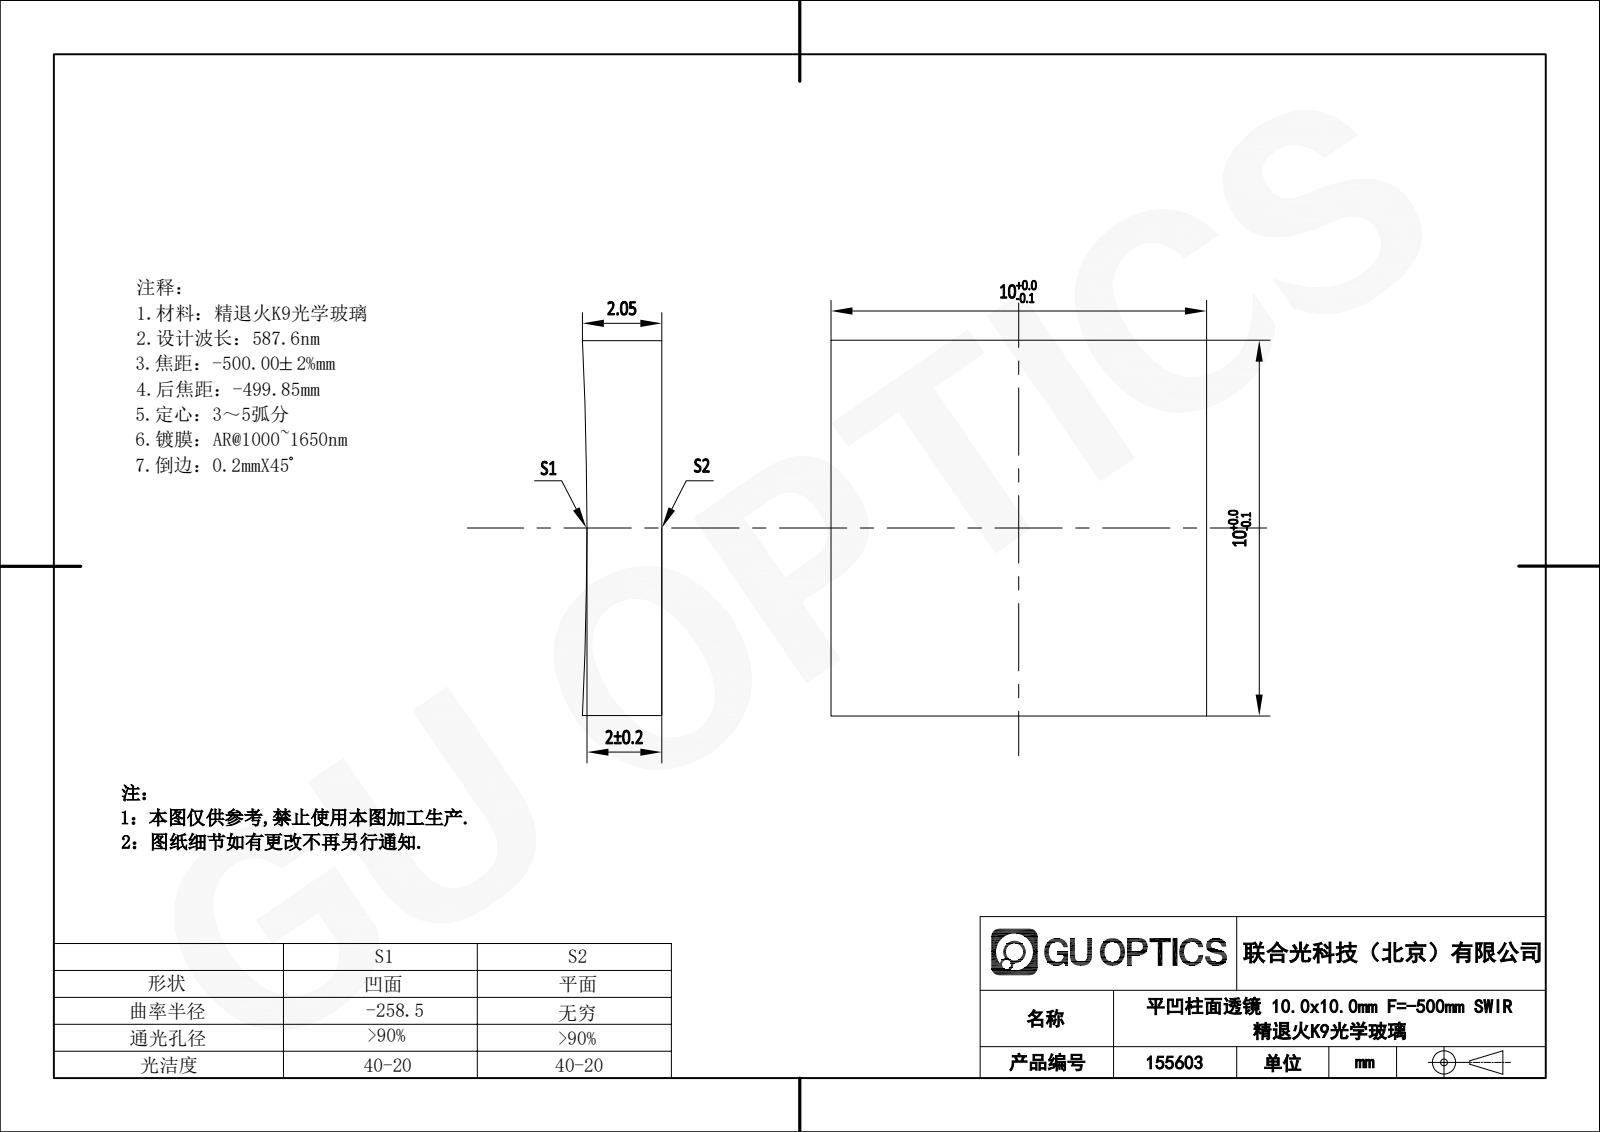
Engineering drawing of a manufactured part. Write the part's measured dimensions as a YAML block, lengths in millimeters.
part_name: "155573"
step_written_by: "SolidWorks 2020 (CONFIG_CONTROL_DESIGN)"
units: millimeters
bodies: {solids: 1, faces: 6, planar: 5, cylindrical: 1, other: 0}
overall_size: [10, 10, 2.05]
volume: 202
surface_area: 281
partial_cylinders:
  - {radius: 258.5, count: 1}
face_to_face_distances: [10]
